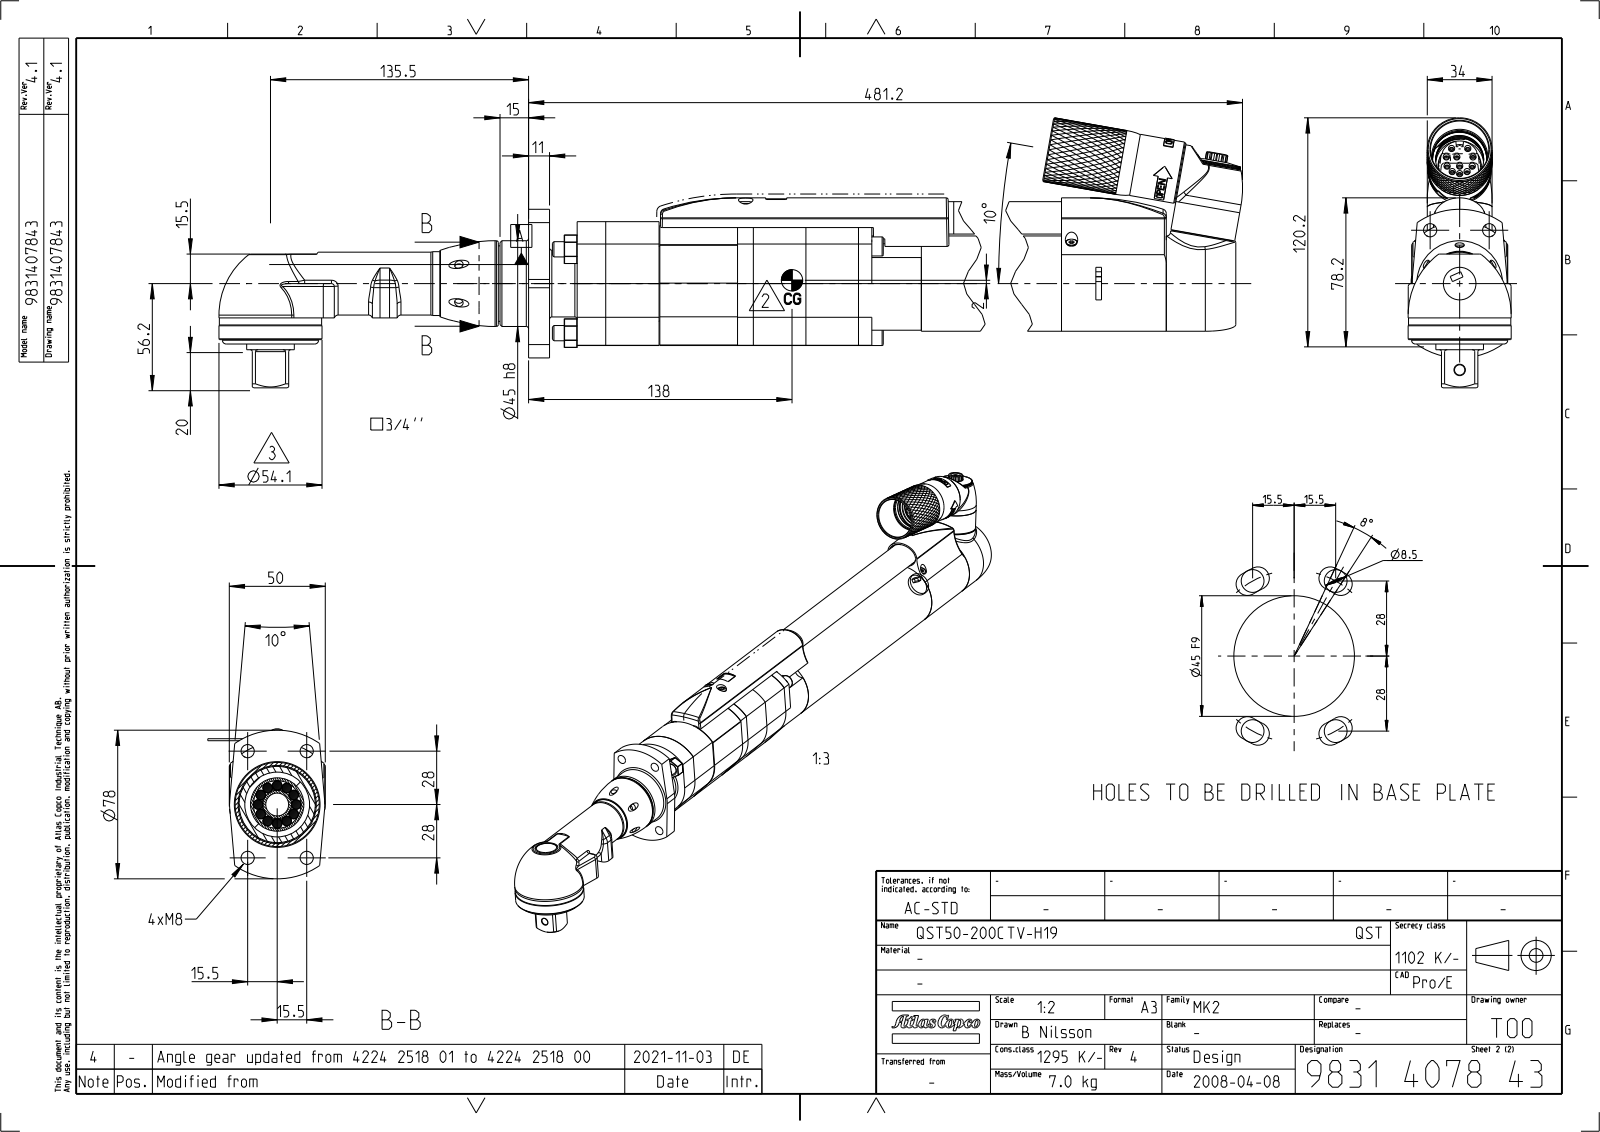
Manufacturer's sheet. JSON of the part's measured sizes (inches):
{"part_name": "EXT_COMP_SW0007", "step_written_by": "CREO PARAMETRIC BY PTC INC, 2022414 (AP242_MANAGED_MODEL_BASED_3D_ENGINEERING_MIM_LF)", "units": "inches", "bodies": {"solids": 1, "faces": 1800, "planar": 740, "cylindrical": 528, "other": 532}, "overall_size": [25.347, 5.579, 2.13], "volume_in3": 84.94, "surface_area_in2": 294.8, "round_holes": [[0.177, 13], [0.315, 8], [0.165, 4], [0.272, 4], [0.194, 3], [0.128, 2], [0.138, 2], [0.256, 2], [0.063, 1], [0.213, 1], [0.276, 1], [0.709, 1]], "round_bosses_or_shafts": [[0.394, 3], [0.315, 3], [0.118, 3], [1.969, 2], [1.339, 2], [0.276, 2], [0.22, 2], [0.157, 2]], "partial_cylinders_radius": [[0.008, 54], [0.02, 34], [0.039, 17], [0.011, 12], [0.02, 12], [0.079, 8], [0.157, 8], [0.059, 5]], "face_to_face_distances": [1.969, 1.693, 0.433, 18.374, 18.807, 2.264, 16.11, 2.697, 0.571, 2.232], "hole_center_spacings": [0.748, 1.058, 1.26, 0.296, 0.344, 0.37, 0.391, 0.419]}
